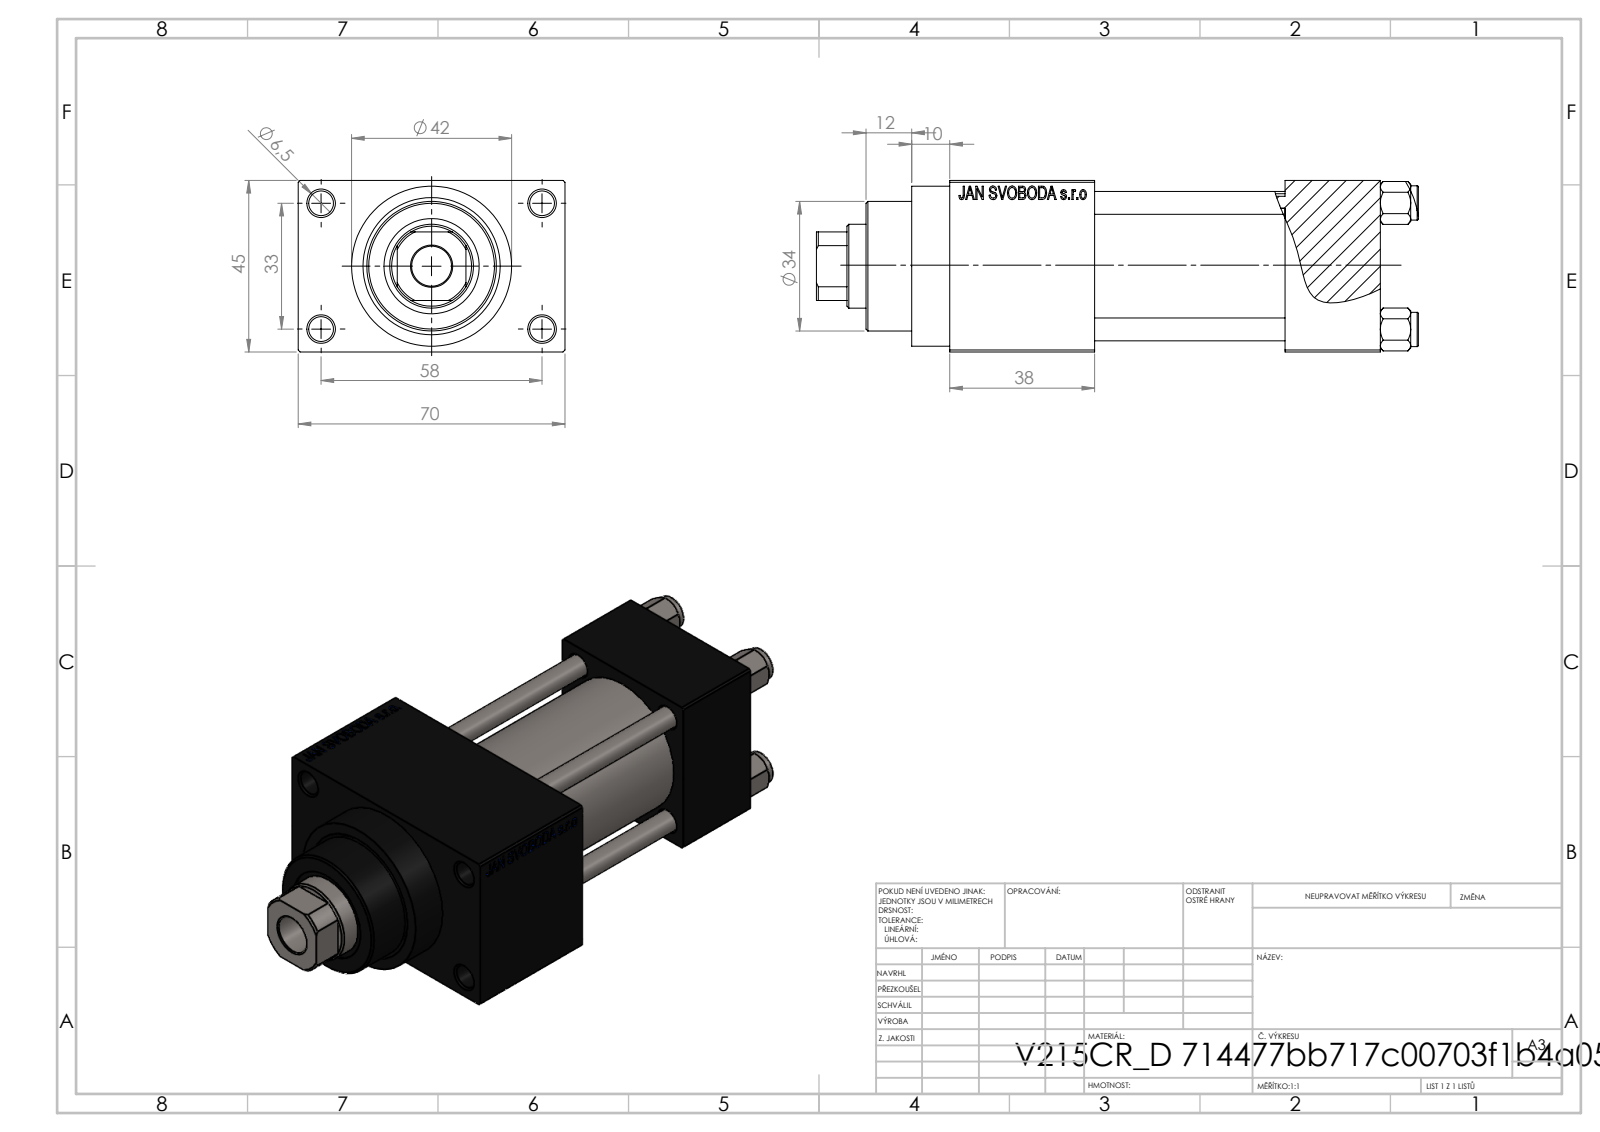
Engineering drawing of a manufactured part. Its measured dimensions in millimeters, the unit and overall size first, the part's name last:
Units: millimetres
Overall size (bounding box): 158 × 70 × 45
Round holes (diameter × count): ⌀6 ×4, ⌀6.5 ×4, ⌀7 ×2, ⌀13.16 ×2, ⌀20 ×2, ⌀10.5 ×1, ⌀22 ×1, ⌀24 ×1, ⌀25 ×1, ⌀32 ×1, ⌀33 ×1
Round bosses / shafts (diameter × count): ⌀9 ×4, ⌀42 ×1, ⌀38 ×1, ⌀34 ×1
Partial cylindrical surfaces — rounded edges, fillets, slot ends (radius × count): R10.5 ×1
Main face-to-face distances: 45, 25, 12.5, 57.5, 50, 75, 88, 70, 38, 113
Hole centre spacings: 12.4, 23.48, 33.2, 33.37, 35.35, 45.6, 56.35, 33
Volume: 244 506 mm³ · Surface area: 79 366 mm²
Bodies: 11 solids, 1105 faces (496 planar, 89 cylindrical, 520 other)
Part name (STEP PRODUCT): NUT_M5_D; V215CR_VCP_D; V215CR_D_TYCINKA; V215CR_D_Body (+1 more)
STEP written by: SolidWorks 2019 (CONFIG_CONTROL_DESIGN)
